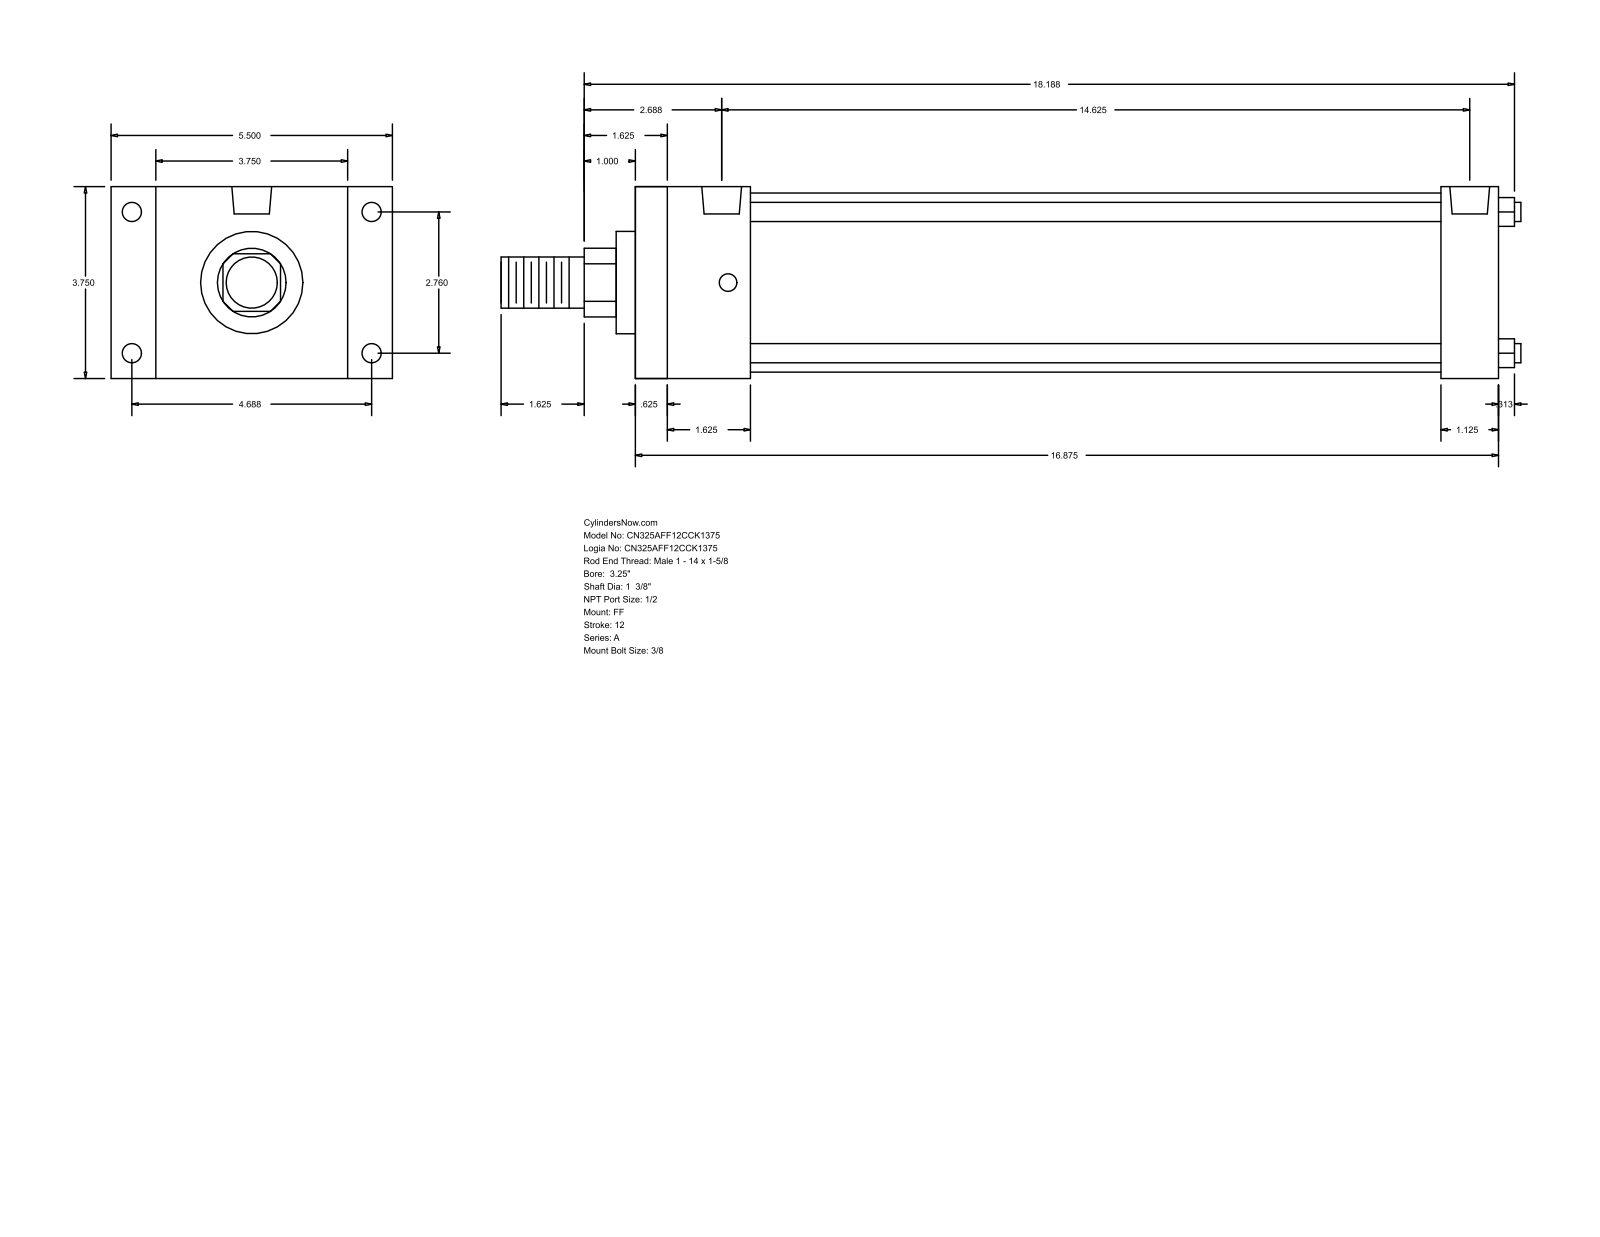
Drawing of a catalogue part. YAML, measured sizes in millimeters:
part_name: "A_FF__0325_1.375"
step_written_by: "GSSL Pune (CONFIG_CONTROL_DESIGN)"
units: millimeters
bodies: {solids: 0, faces: 92, planar: 64, cylindrical: 28, other: 0}
overall_size: [506.41, 139.7, 95.25]
round_holes:
  - {diameter: 8.73, count: 4}
  - {diameter: 9.53, count: 4}
  - {diameter: 19.77, count: 2}
round_bosses_or_shafts:
  - {diameter: 9.53, count: 4}
  - {diameter: 88.9, count: 1}
  - {diameter: 50.8, count: 1}
  - {diameter: 34.92, count: 1}
  - {diameter: 25.4, count: 1}
partial_cylinders:
  - {radius: 17.06, count: 1}
face_to_face_distances: [95.24, 428.62, 412.75, 15.87, 57.15, 22.23, 117.47, 28.57, 400.05, 41.28]
hole_center_spacings: [3.18, 70.1, 119.06, 138.16, 365.12, 368.3, 371.48]
